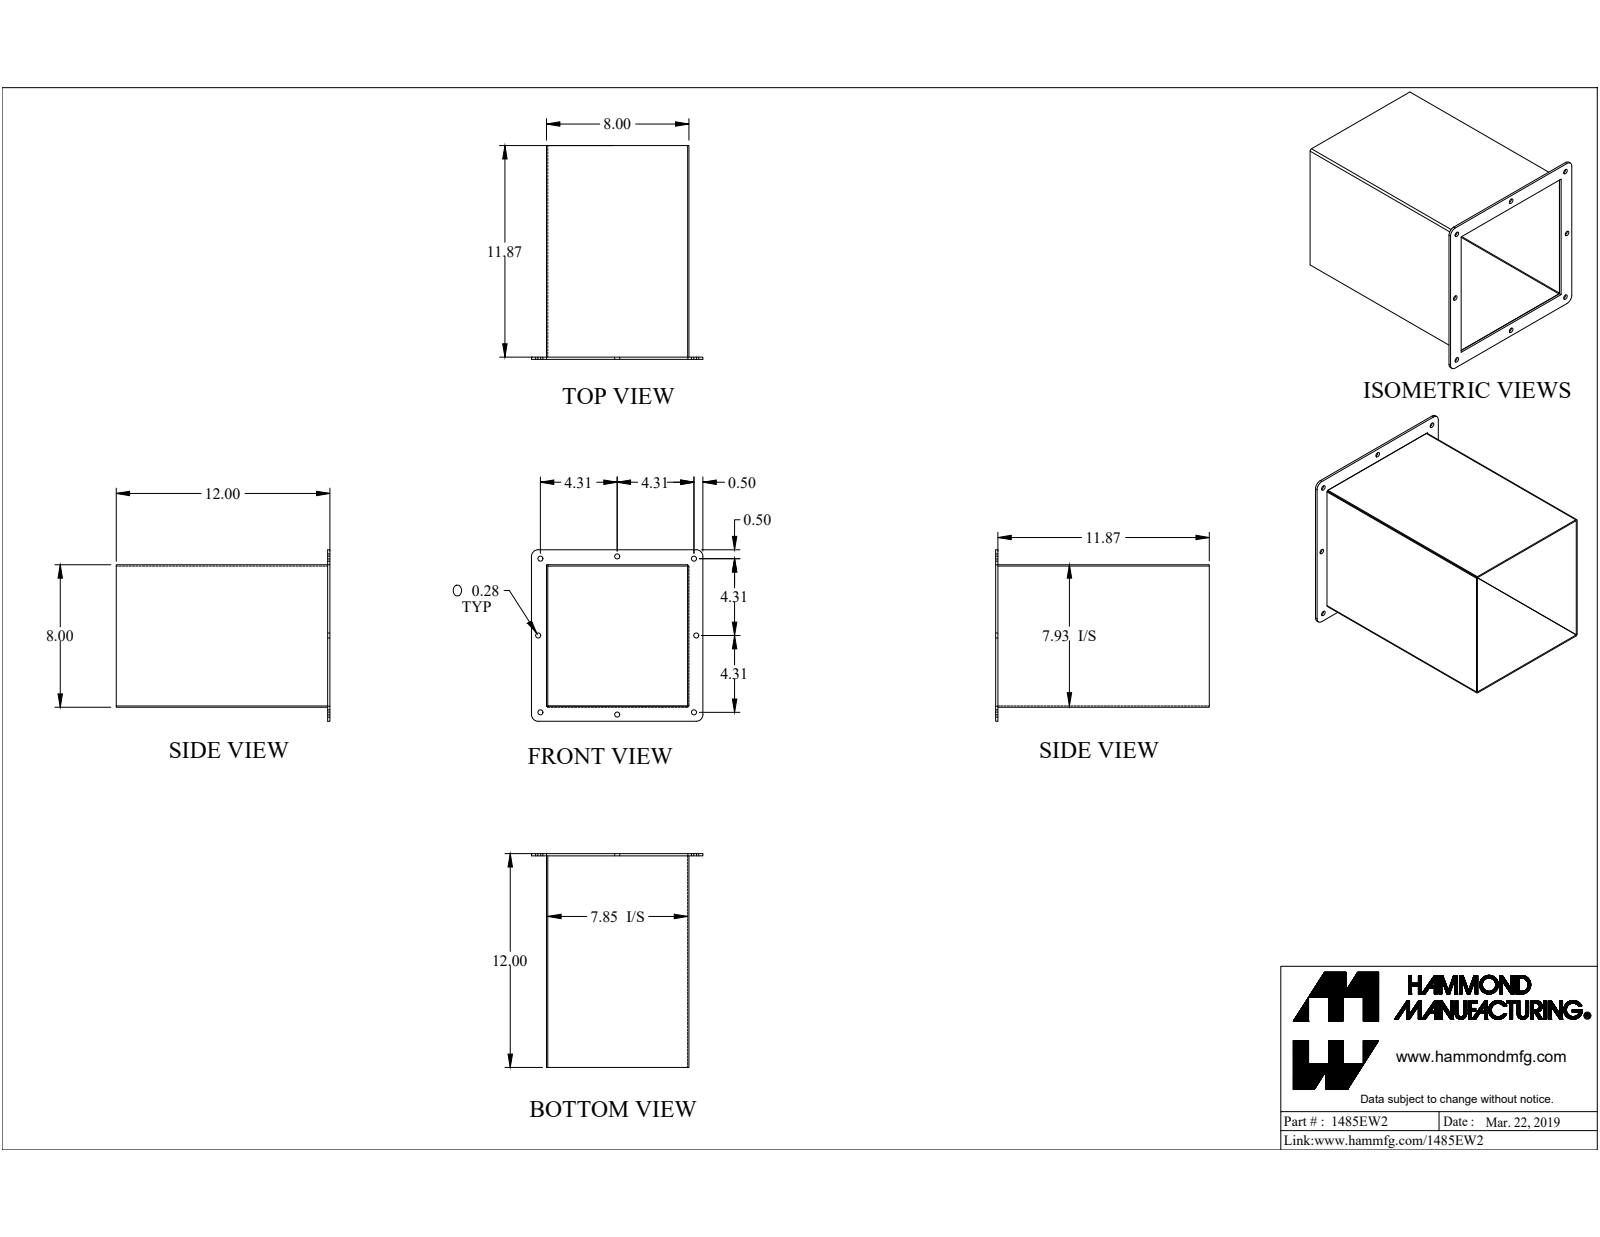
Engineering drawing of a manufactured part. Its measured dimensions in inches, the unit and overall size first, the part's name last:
Units: inches
Overall size (bounding box): 12.125 × 9.625 × 9.625
Round holes (diameter × count): ⌀0.281 ×8
Partial cylindrical surfaces — rounded edges, fillets, slot ends (radius × count): R0.375 ×4, R0.036 ×2, R0.108 ×2
Main face-to-face distances: 0.072, 7.853, 7.925, 0.072, 7.925, 7.997, 12, 0.125, 12.125, 11.875
Hole centre spacings: 4.314, 4.315, 8.625, 9.755, 9.755, 6.276, 8.875, 12.197
Volume: 34.17 in³ · Surface area: 891 in²
Bodies: 4 solids, 64 faces (36 planar, 28 cylindrical, 0 other)
Part name (STEP PRODUCT): 1485EW2
STEP written by: SolidWorks 2019 (CONFIG_CONTROL_DESIGN)
